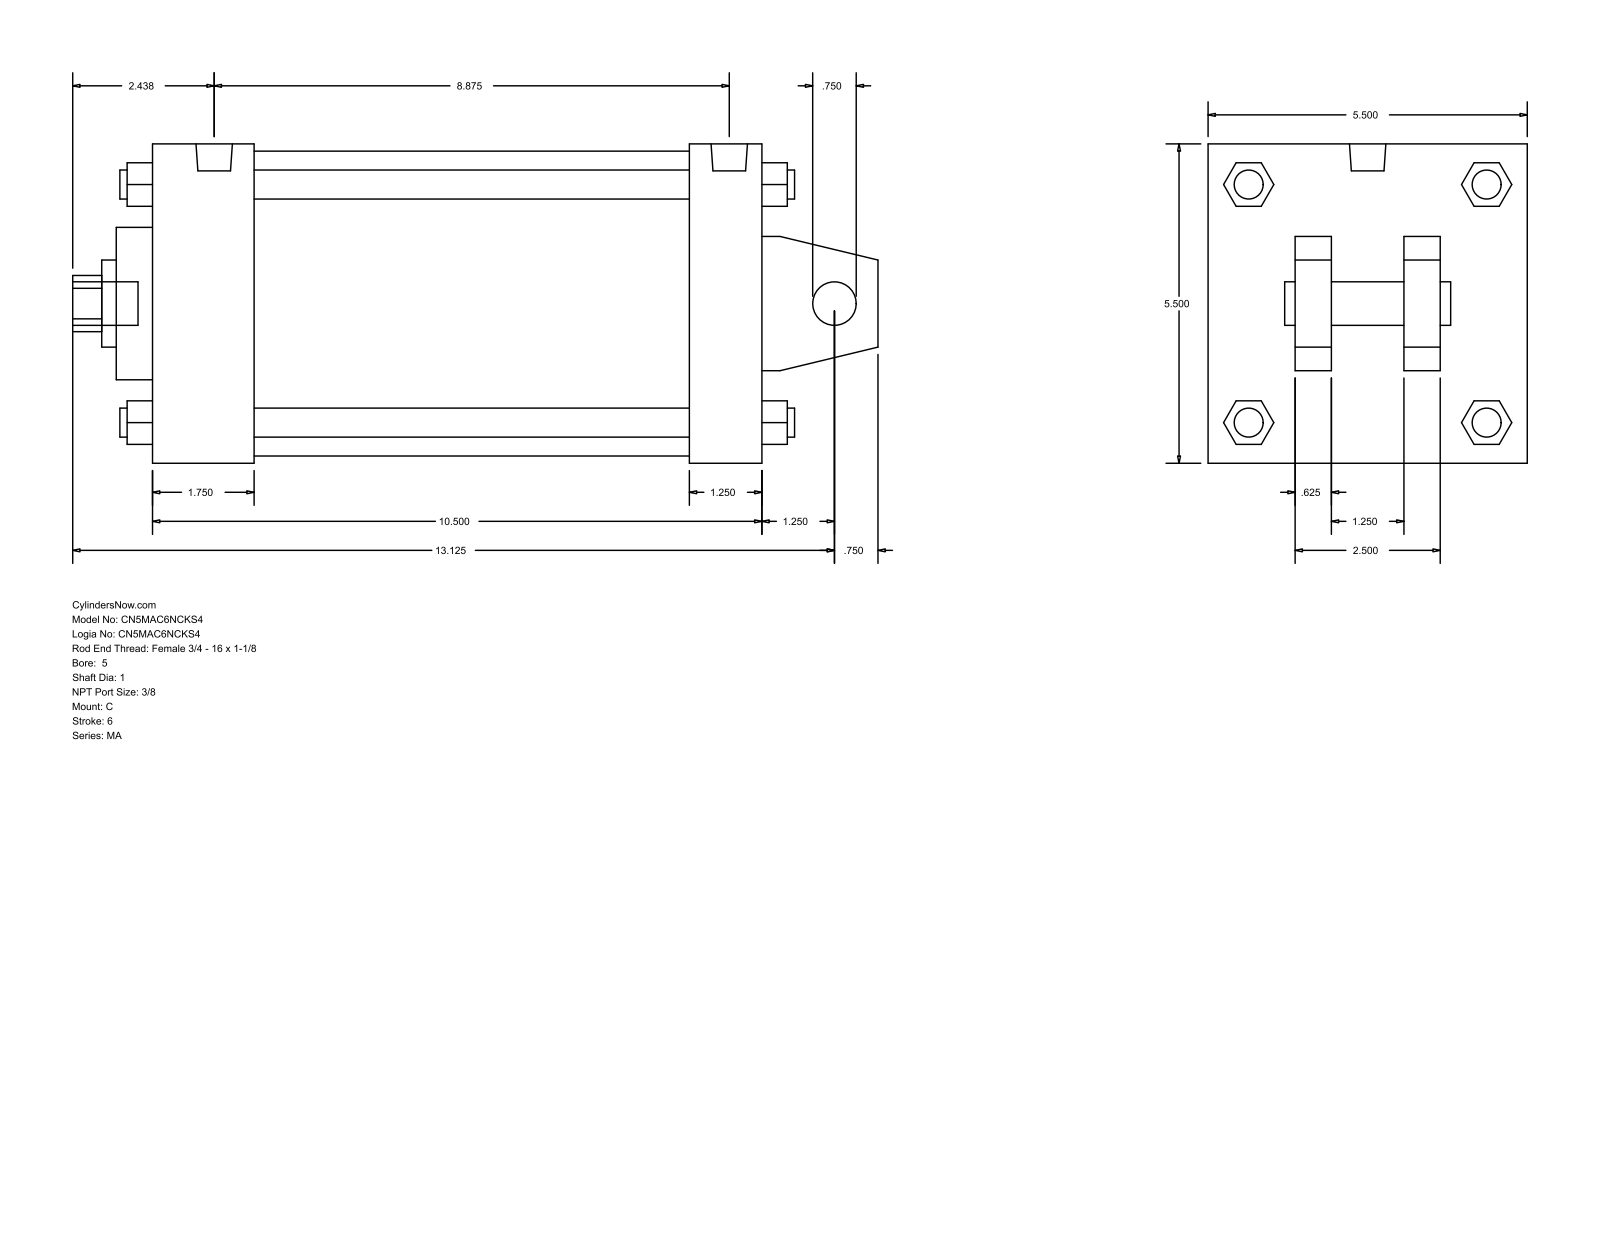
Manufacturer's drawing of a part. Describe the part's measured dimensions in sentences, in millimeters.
The part is named "MA_C__0500_1". Its 3-D file was written by "GSSL Pune (CONFIG_CONTROL_DESIGN)". It is 0 solids with 141 faces: 109 planar, 32 cylindrical and 0 other. Overall it measures 352.43 by 139.7 by 139.7 millimeters. Round holes: 1 of diameter 19.05, 1 of diameter 25.4, 1 of diameter 38.1, 1 of diameter 66.67, 1 of diameter 133.35. Round bosses or shafts: 4 of diameter 12.7, 4 of diameter 11.11, 2 of diameter 15.93, 1 of diameter 19.05. Partial cylindrical surfaces (rounded edges, fillets, slot ends): 1 of radius 12.29. The main face-to-face distances are 139.7, 266.7, 15.87, 234.96, 31.74, 44.46, 190.5, 222.24, 38.1, 101.6.
